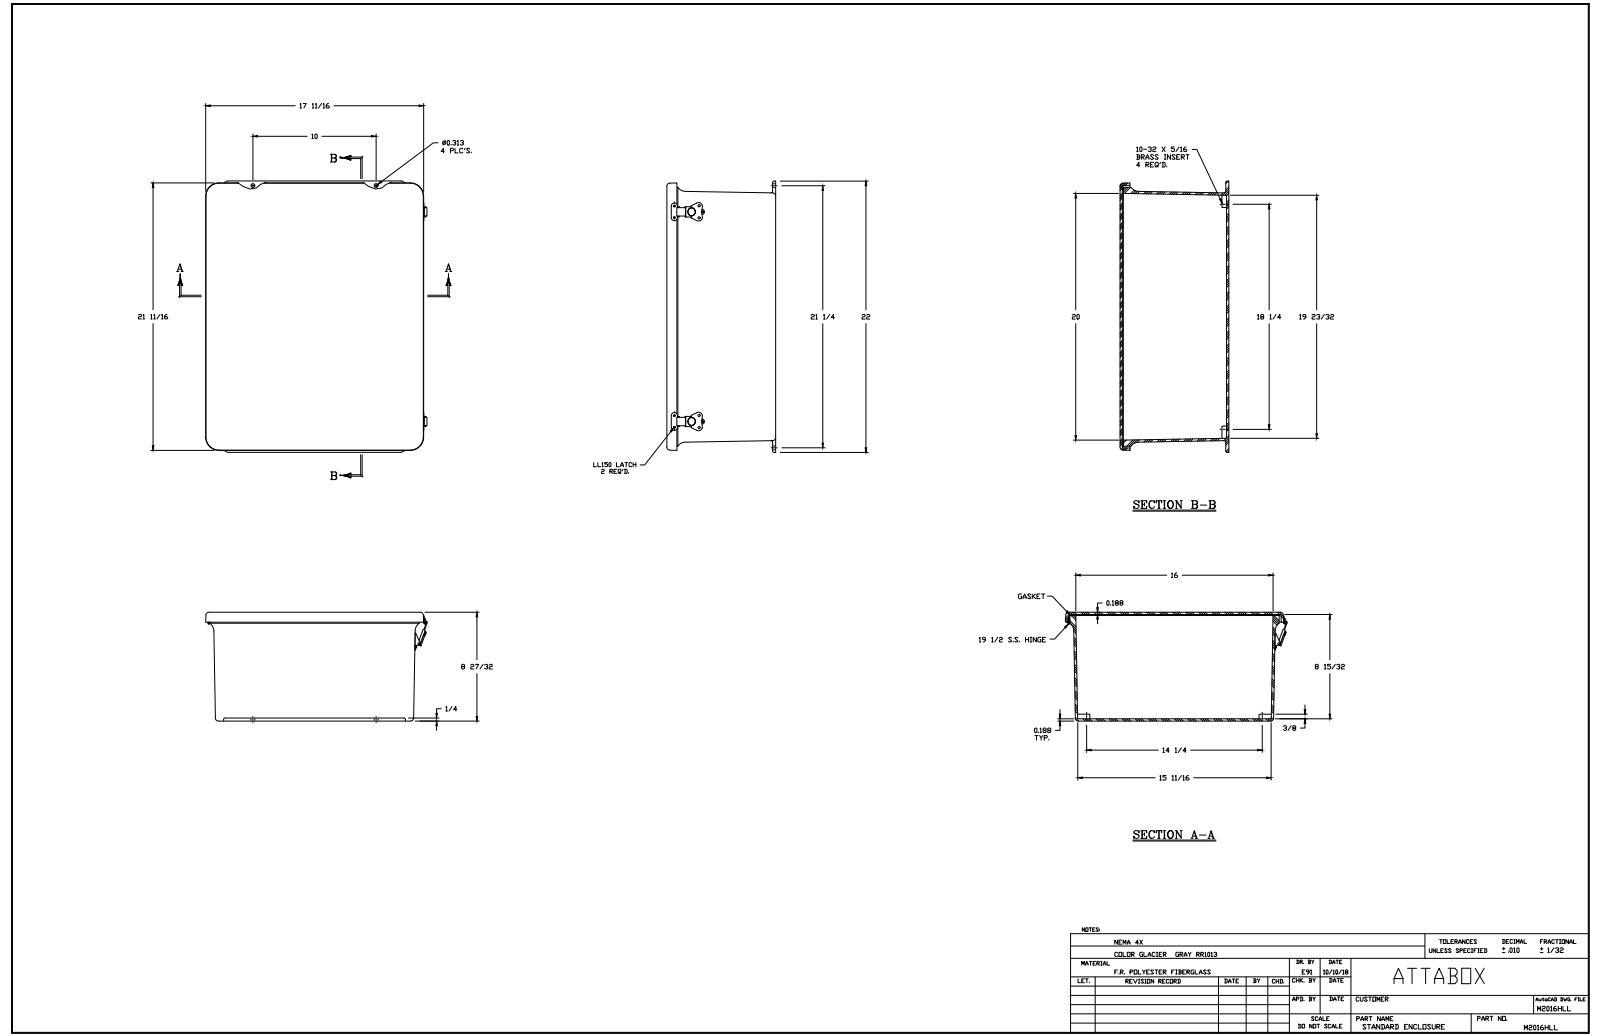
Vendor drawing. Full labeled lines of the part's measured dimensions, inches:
Part name (STEP PRODUCT): M2016HLL
STEP written by: SolidWorks 2018 (AUTOMOTIVE_DESIGN)
Units: inches
Bodies: 50 solids, 1197 faces (571 planar, 497 cylindrical, 129 other)
Overall size (bounding box): 22 × 17.904 × 8.829
Volume: 283.6 in³ · Surface area: 2 971 in²
Round holes (diameter × count): ⌀0.14 ×22, ⌀0.131 ×12, ⌀0.152 ×5, ⌀0.104 ×4, ⌀0.13 ×4, ⌀0.133 ×4, ⌀0.156 ×4, ⌀0.187 ×4, ⌀0.218 ×4, ⌀0.135 ×2, ⌀0.189 ×2, ⌀0.191 ×2
Round bosses / shafts (diameter × count): ⌀0.25 ×16, ⌀0.125 ×12, ⌀0.125 ×10, ⌀0.27 ×4, ⌀0.66 ×2, ⌀0.582 ×2, ⌀0.525 ×2, ⌀0.286 ×2
Partial cylindrical surfaces — rounded edges, fillets, slot ends (radius × count): R0.031 ×20, R0.015 ×16, R0.06 ×13, R0.125 ×11, R0.25 ×10, R0.011 ×8, R0.02 ×8, R0.07 ×8
Main face-to-face distances: 0.187, 8.642, 8.829, 0.188, 8.454, 8.641, 0.313, 0.5, 0.267, 0.079
Hole centre spacings: 17, 3.75, 7.5, 0.851, 0.25, 0.281, 0.938, 3.5
